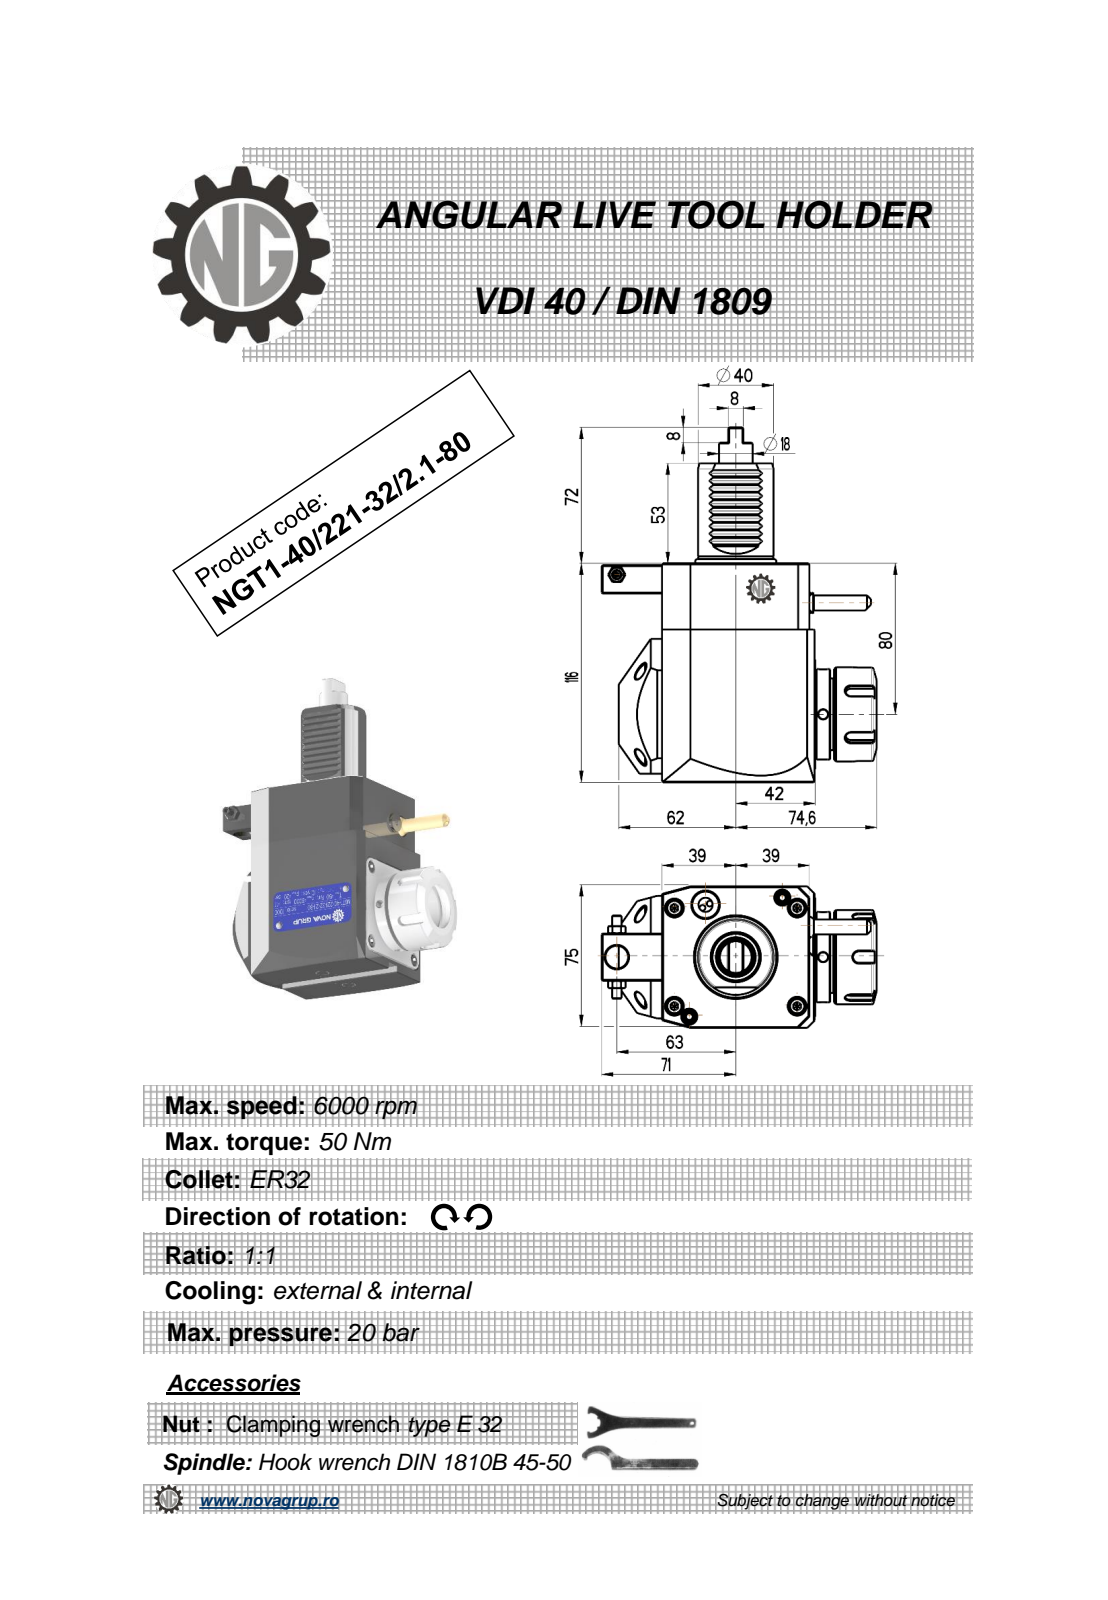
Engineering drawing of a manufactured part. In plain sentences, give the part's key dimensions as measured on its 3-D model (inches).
The part is named "NGT1_40_221_32_2_1_80". Its 3-D file was written by "PRO/ENGINEER BY PARAMETRIC TECHNOLOGY CORPORATION, 2010280 (CONFIG_CONTROL_DESIGN)". It is 1 solid with 415 faces: 199 planar, 89 cylindrical and 127 other. Overall it measures 7.402 by 5.732 by 3.016 inches. Its volume is 53.89 cubic inches and its surface area 109.1 square inches. Round holes: 3 of diameter 0.197, 1 of diameter 0.118, 1 of diameter 0.165, 1 of diameter 0.374, 1 of diameter 0.472, 1 of diameter 1.063. Round bosses or shafts: 1 of diameter 1.969, 1 of diameter 1.89, 1 of diameter 1.614, 1 of diameter 1.575, 1 of diameter 0.701, 1 of diameter 0.441, 1 of diameter 0.353, 1 of diameter 0.315. Partial cylindrical surfaces (rounded edges, fillets, slot ends): 12 of radius 0.01, 10 of radius 0.012, 6 of radius 0.009, 5 of radius 0.118, 2 of radius 0.031, 1 of radius 0.02, 1 of radius 1.575. The main face-to-face distances are 2.953, 4.567, 3.189, 0.118, 3.071, 3.181, 0.11, 4.409, 0.984, 0.295. The hole center spacings are 0.824, 2.407, 2.854, 4.301, 5.195.
